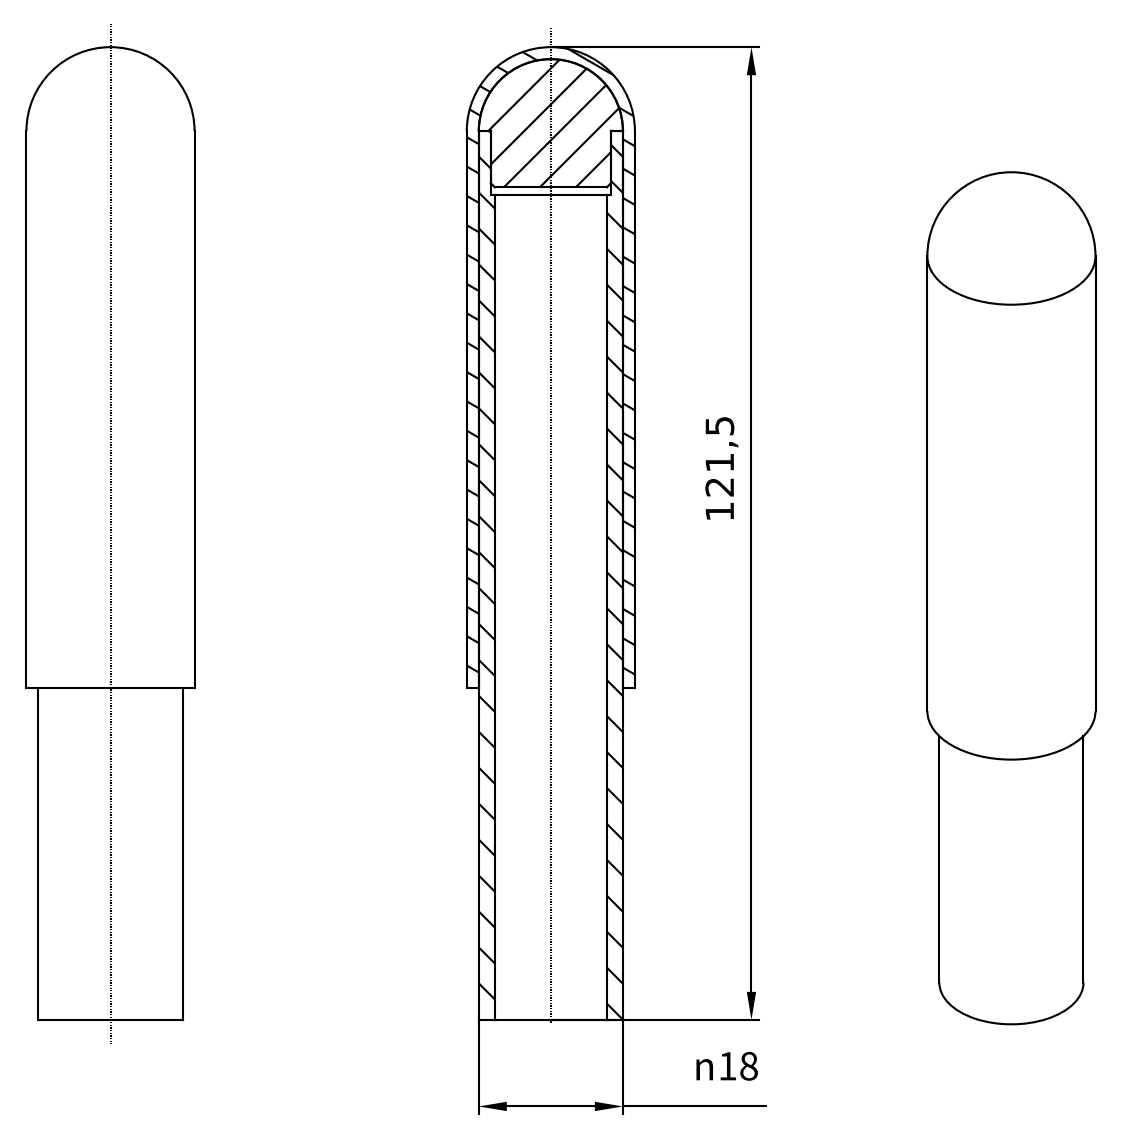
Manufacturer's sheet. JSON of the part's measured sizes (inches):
{"step_written_by": "Autodesk Inventor 8 (AUTOMOTIVE_DESIGN)", "units": "inches", "bodies": {"solids": 1, "faces": 16, "planar": 4, "cylindrical": 8, "other": 4}, "overall_size": [4.783, 0.827, 0.827], "volume_in3": 1.283, "surface_area_in2": 19.57, "round_holes": [[0.551, 1], [0.591, 1]], "round_bosses_or_shafts": [[0.827, 1], [0.709, 1]], "face_to_face_distances": [4.094, 1.634, 2.461, 4.055, 2.421, 0.039]}
